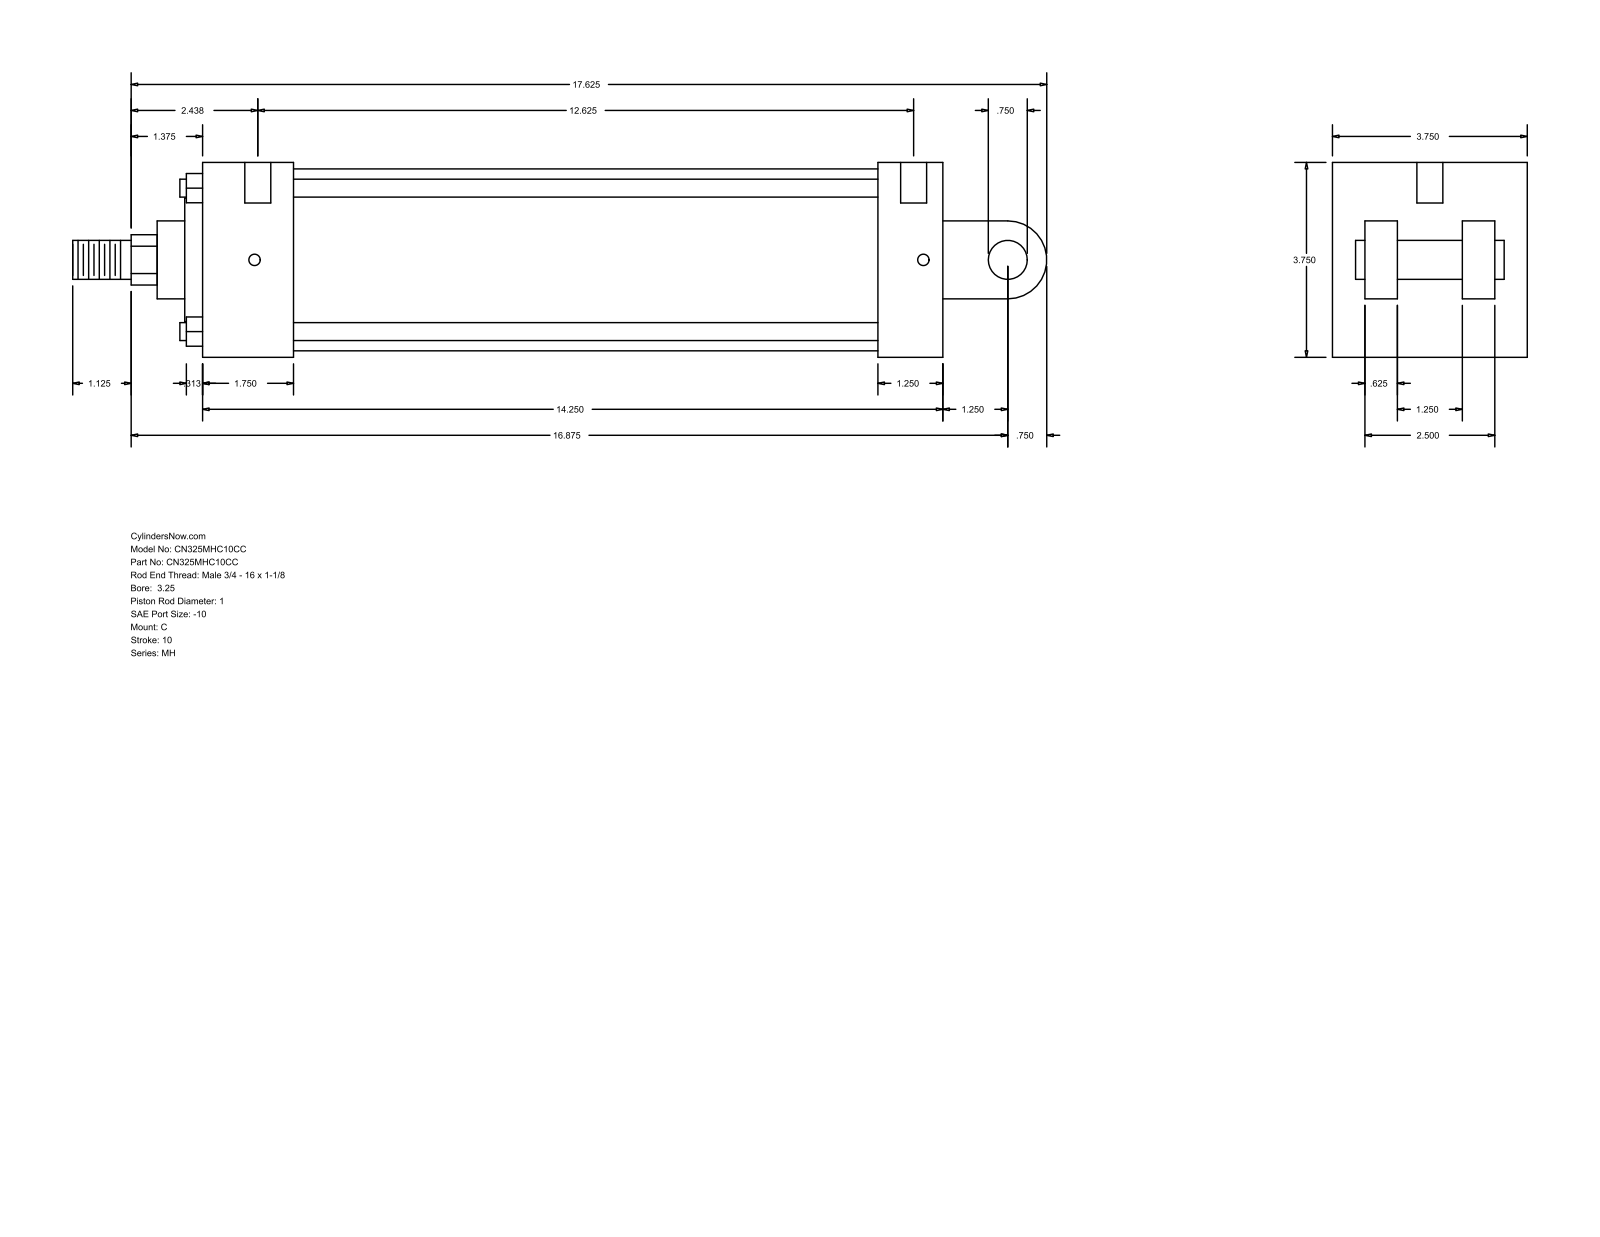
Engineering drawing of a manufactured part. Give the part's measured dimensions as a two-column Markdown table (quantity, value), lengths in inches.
| quantity | value |
| --- | --- |
| part name | MH_C__0325_1 |
| STEP written by | GSSL Pune (CONFIG_CONTROL_DESIGN) |
| units | inches |
| bodies | 0 solids, 101 faces (71 planar, 30 cylindrical, 0 other) |
| overall size | 18.75 × 3.75 × 3.75 |
| round holes (diameter × count) | 0.219 × 4, 0.5 × 2 |
| round bosses / shafts (diameter × count) | 0.345 × 4, 0.75 × 2, 3.5 × 1, 2.375 × 1, 1.5 × 1, 1 × 1 |
| partial cylindrical surfaces (radius × count) | 0.484 × 1, 0.75 × 1 |
| main face-to-face distances | 3.75, 0.625, 14.25, 2.5, 1.25, 3.125, 1.25, 1.875, 1.75, 13 |
| hole center spacings | 12.875, 0.062, 0.187, 12.625, 12.687, 12.813 |
